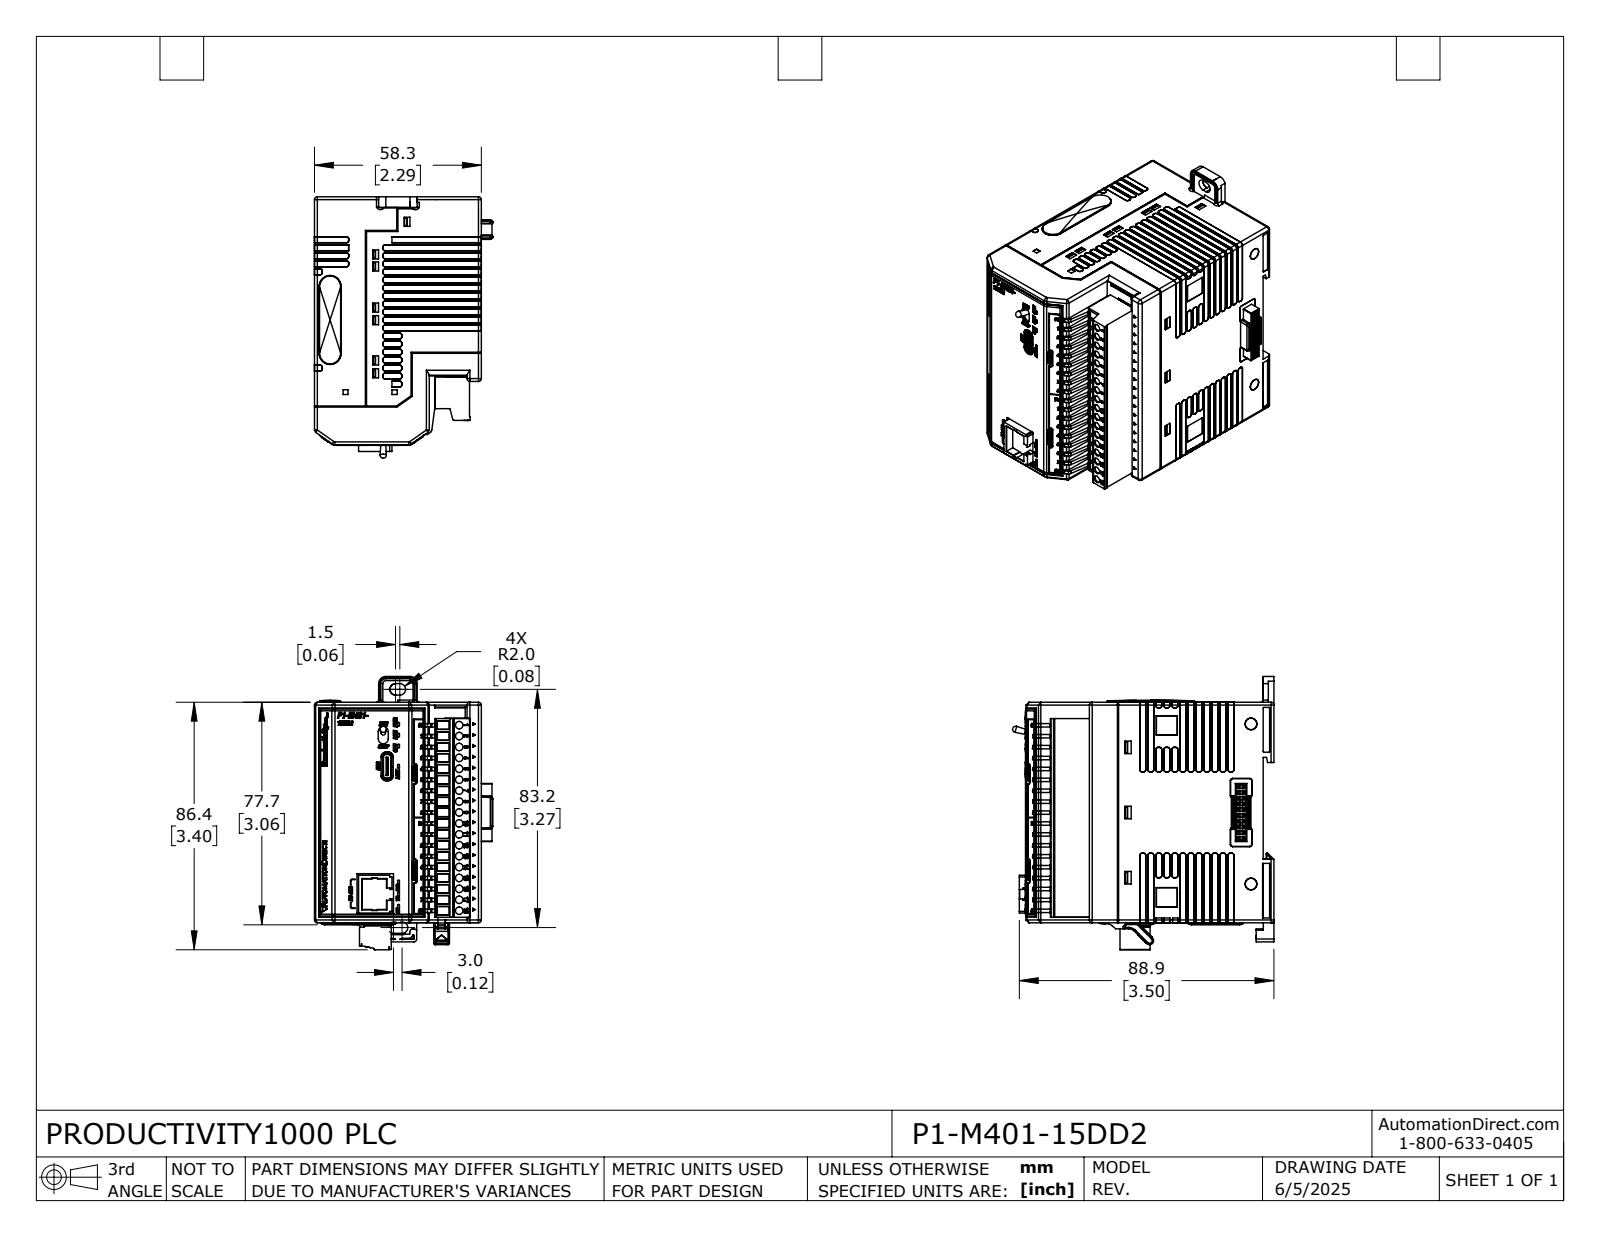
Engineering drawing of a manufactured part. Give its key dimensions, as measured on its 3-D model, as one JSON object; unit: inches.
{"part_name": "P1-M401-15DD2", "step_written_by": "SolidWorks 2024 (AUTOMOTIVE_DESIGN)", "units": "inches", "bodies": {"solids": 21, "faces": 3495, "planar": 1950, "cylindrical": 875, "other": 670}, "overall_size": [3.686, 3.593, 2.452], "volume_in3": 2.075, "surface_area_in2": 102.9, "partial_cylinders_radius": [[0.01, 172], [0.008, 78], [0.02, 53], [0.039, 33], [0.004, 10], [0.079, 8], [0.024, 7], [0.012, 4]], "face_to_face_distances": [2.235, 0.02, 0.039, 2.275, 3.01, 3.022, 2.294, 2.294, 2.255, 3.02]}
